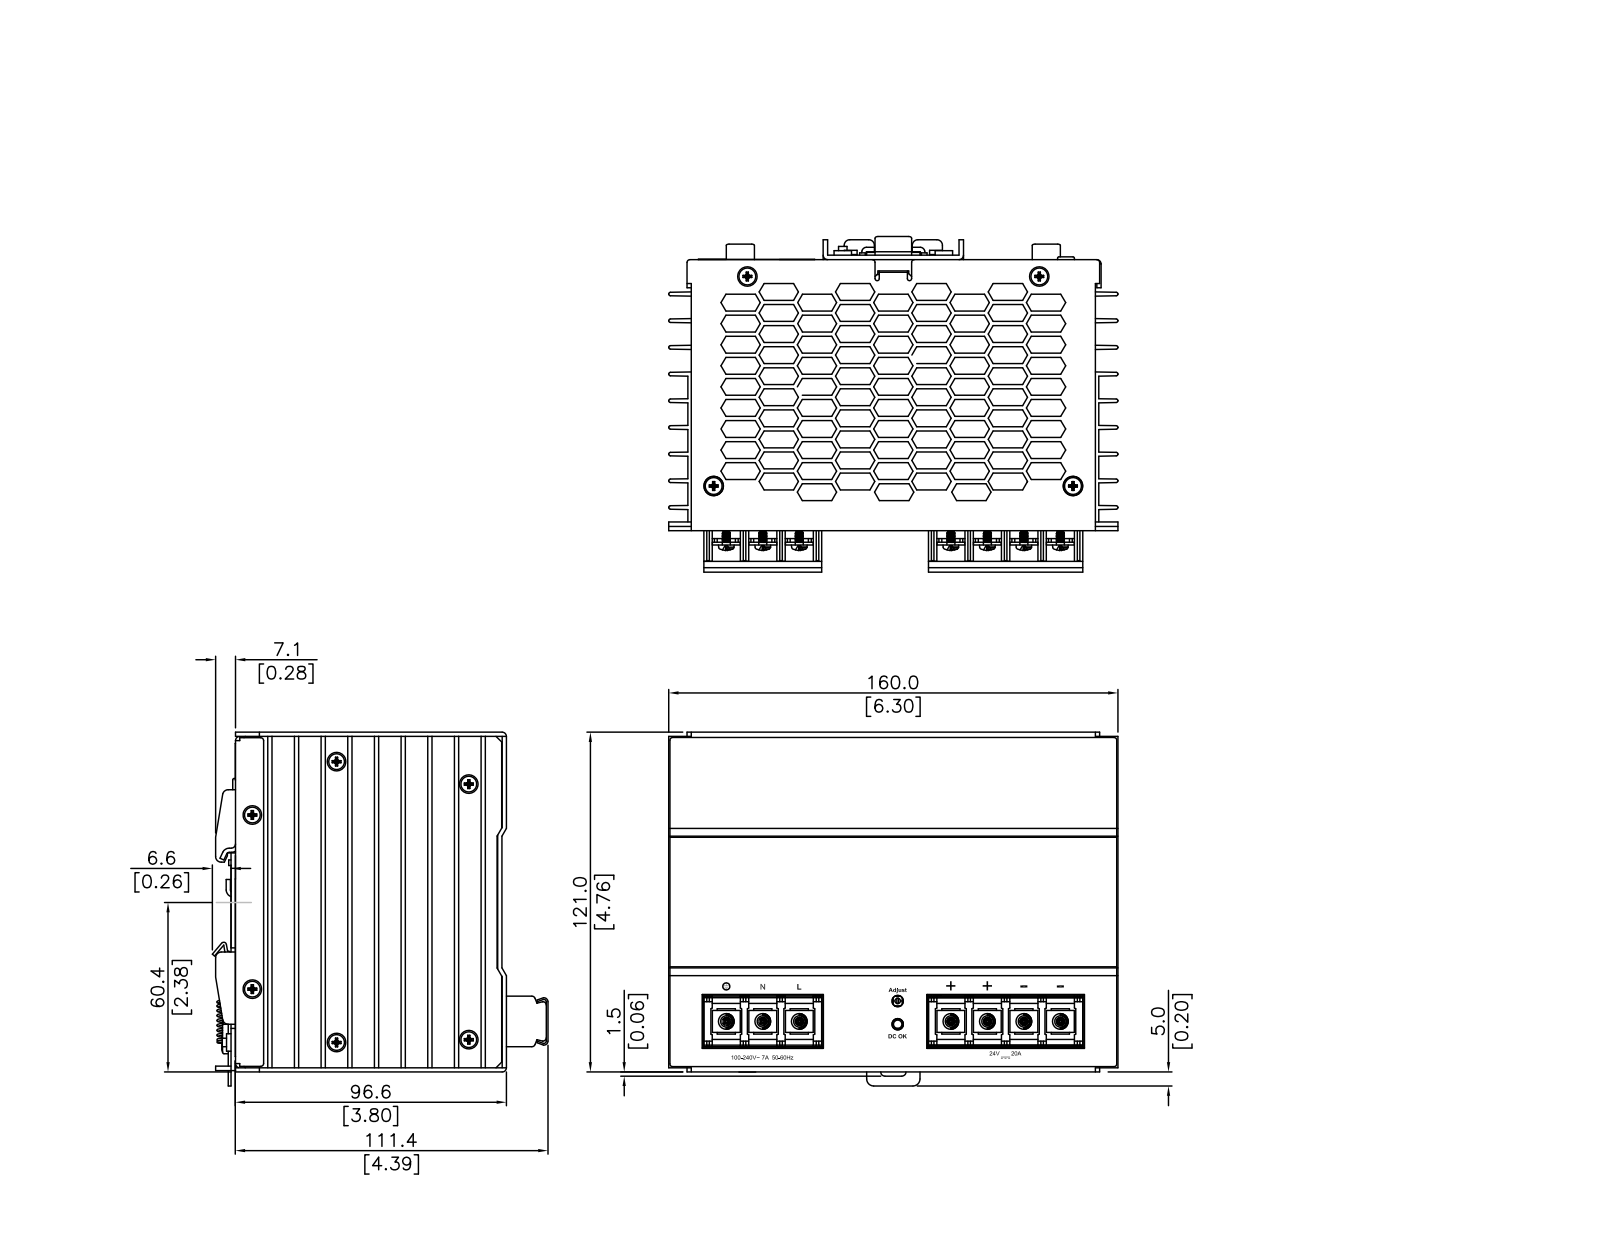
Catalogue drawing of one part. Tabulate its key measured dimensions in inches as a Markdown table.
| quantity | value |
| --- | --- |
| part name | PSB24-480 |
| STEP written by | SolidWorks 2011 (CONFIG_CONTROL_DESIGN) |
| units | inches |
| bodies | 1 solid, 1991 faces (1767 planar, 142 cylindrical, 82 other) |
| overall size | 6.3 × 4.946 × 4.612 |
| volume | 101.1 in³ |
| surface area | 342.8 in² |
| round holes (diameter × count) | 0.16 × 2 |
| round bosses / shafts (diameter × count) | 0.22 × 7, 0.125 × 2 |
| partial cylindrical surfaces (radius × count) | 0.02 × 36, 0.03 × 27, 0.06 × 12, 0.04 × 3, 0.05 × 3, 0.016 × 2, 0.04 × 2, 0.075 × 2 |
| main face-to-face distances | 0.37, 0.075, 3.652, 3.577, 0.165, 3.626, 0.09, 3.487, 3.552, 3.461 |
| hole center spacings | 0.4 |
